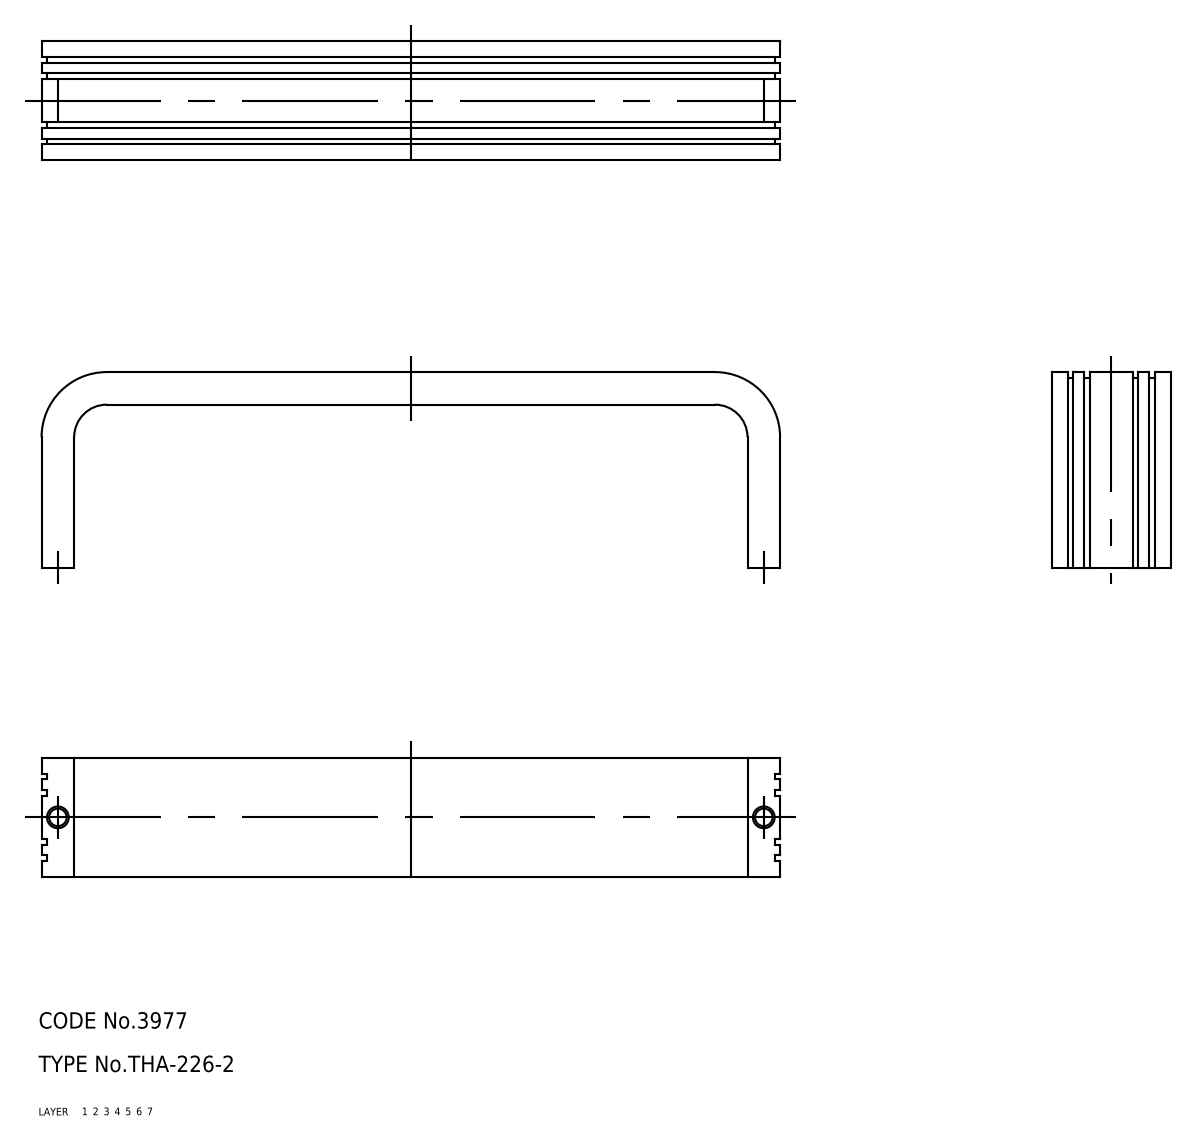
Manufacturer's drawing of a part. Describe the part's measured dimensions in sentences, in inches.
The part is named "pull". Its 3-D file was written by "CADfix (AUTOMOTIVE_DESIGN)". It is 1 solid with 68 faces: 0 planar, 0 cylindrical and 68 other. Overall it measures 5.354 by 1.417 by 0.866 inches. Its volume is 1.46 cubic inches and its surface area 19.39 square inches.
